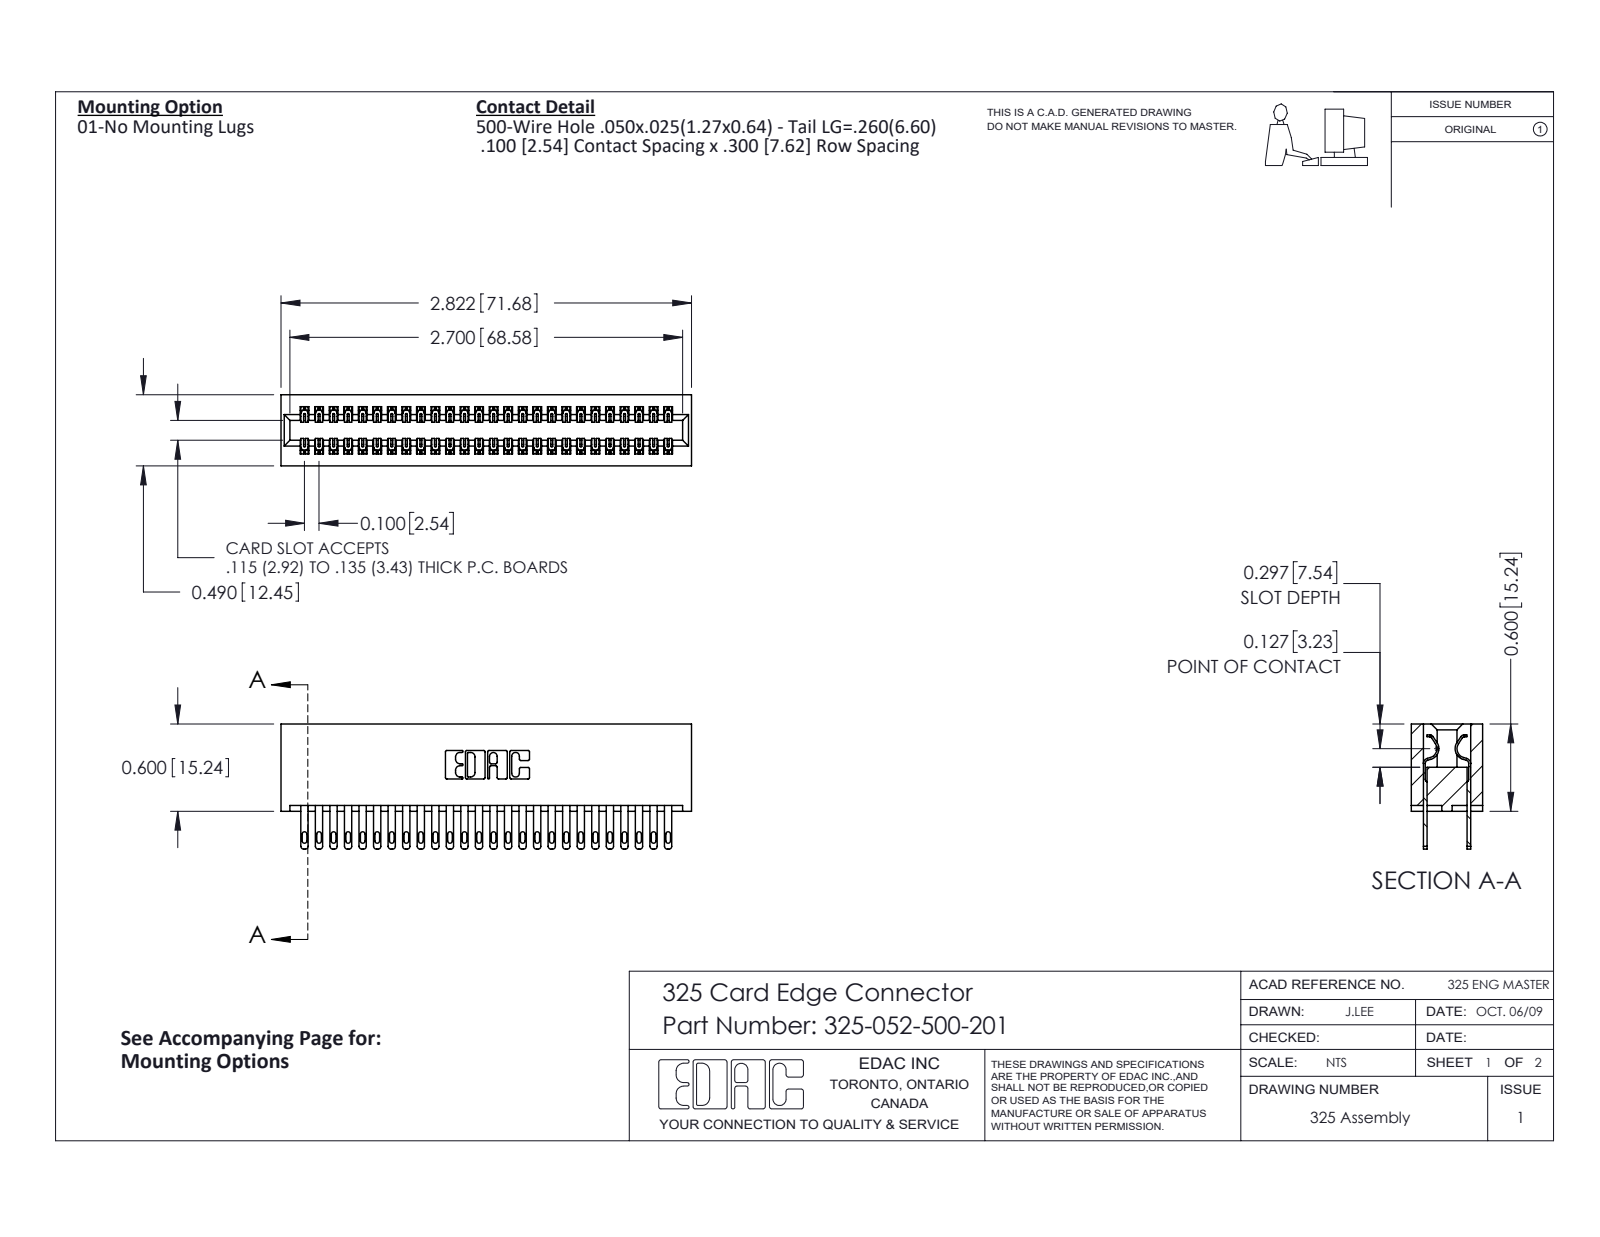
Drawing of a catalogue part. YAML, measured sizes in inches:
part_name: "325-292-001_325-293-100; 325-052-500-201; 325 Part_Lugless"
step_written_by: "SolidWorks 2016 (CONFIG_CONTROL_DESIGN)"
units: inches
bodies: {solids: 53, faces: 2602, planar: 1626, cylindrical: 976, other: 0}
overall_size: [2.822, 0.86, 0.49]
volume: 0.603
surface_area: 19.81
partial_cylinders:
  - {radius: 0.006, count: 78}
  - {radius: 0.016, count: 52}
  - {radius: 0.02, count: 52}
  - {radius: 0.01, count: 22}
  - {radius: 0.007, count: 6}
  - {radius: 0.031, count: 6}
  - {radius: 0.026, count: 3}
  - {radius: 0.014, count: 2}
face_to_face_distances: [0.083, 0.407, 0.3, 0.107, 0.383, 0.025, 0.325, 0.49, 0.275, 0.56]
